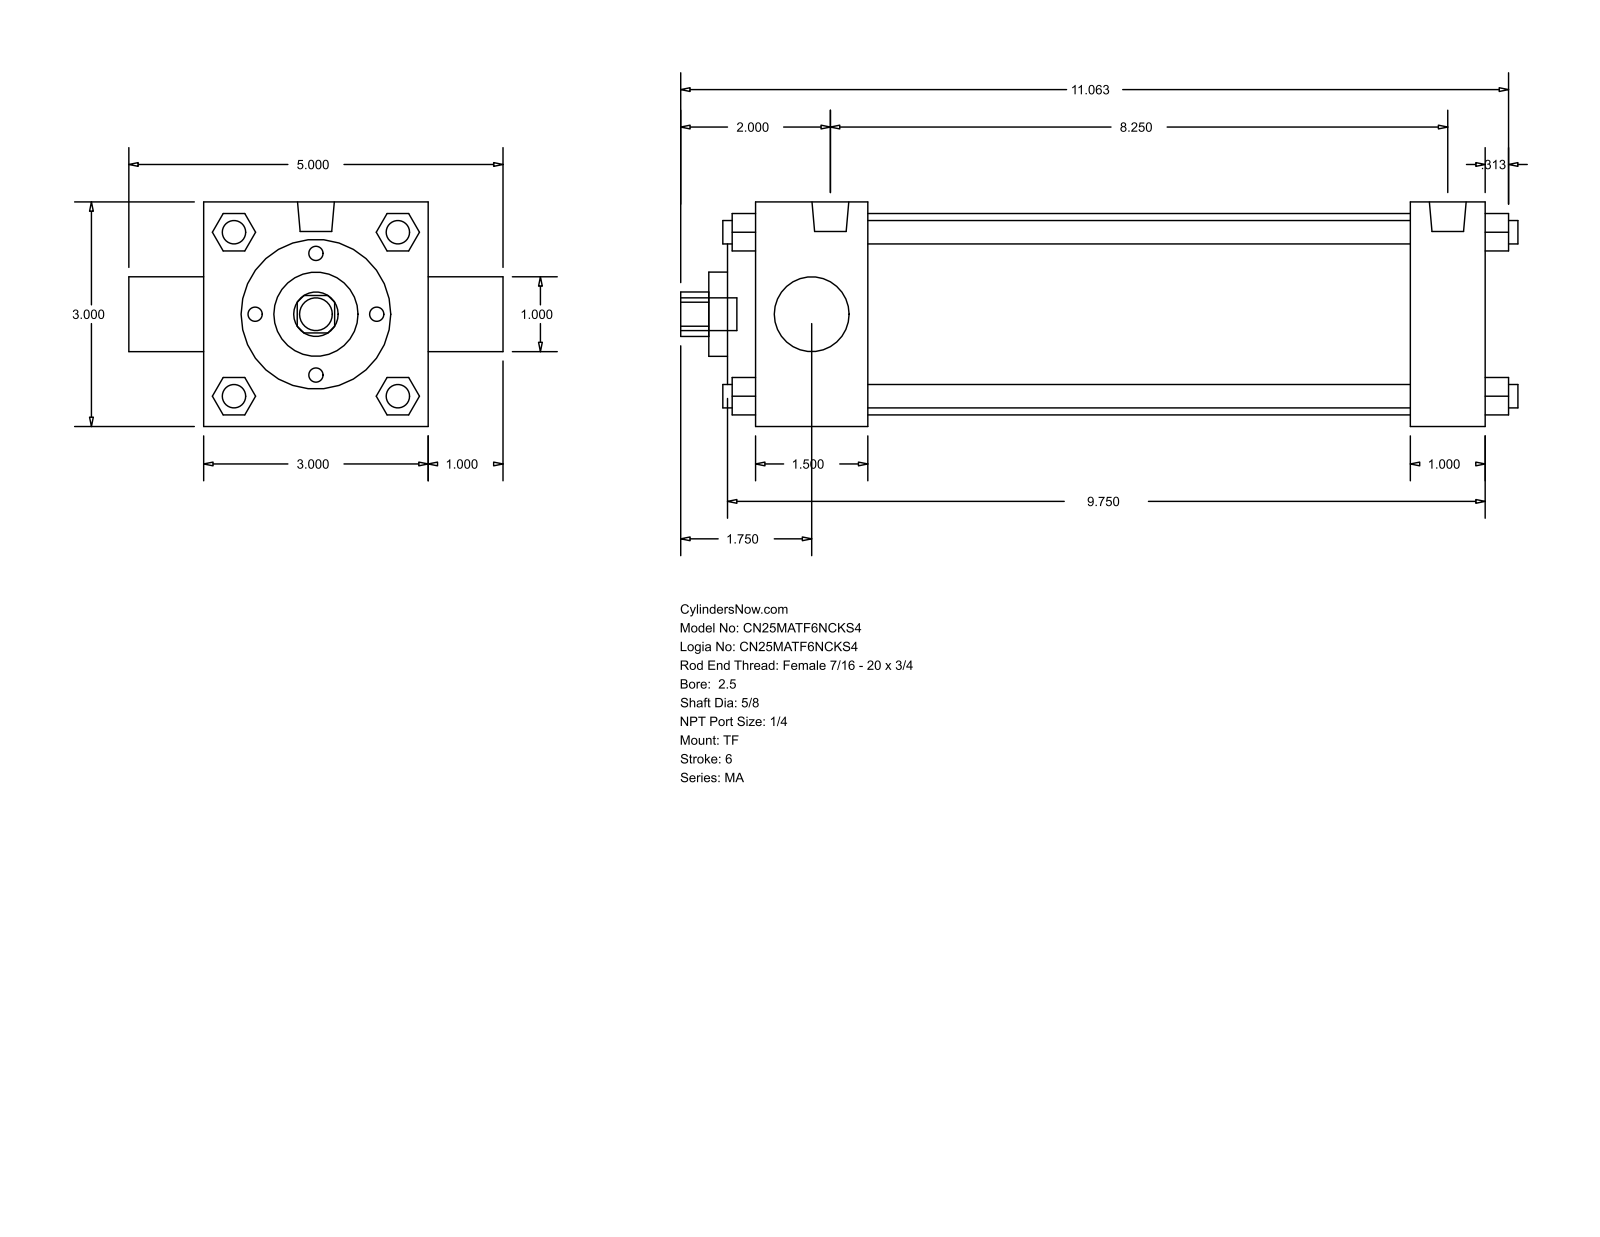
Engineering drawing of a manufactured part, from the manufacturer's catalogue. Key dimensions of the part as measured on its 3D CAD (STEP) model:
Part name (STEP PRODUCT): MA_TF__0250_0.625
STEP written by: GSSL Pune (CONFIG_CONTROL_DESIGN)
Units: millimetres
Bodies: 0 solids, 122 faces (93 planar, 29 cylindrical, 0 other)
Overall size (bounding box): 284.16 × 127 × 76.2
Round holes (diameter × count): ⌀15.88 ×1, ⌀25.4 ×1, ⌀28.57 ×1, ⌀50.8 ×1, ⌀68.33 ×1
Round bosses / shafts (diameter × count): ⌀7.94 ×7, ⌀12.49 ×2, ⌀11.11 ×1
Partial cylindrical surfaces — rounded edges, fillets, slot ends (radius × count): R7.54 ×1
Main face-to-face distances: 76.2, 247.65, 25.4, 38.1, 222.25, 184.15, 209.55, 12.7, 9.52, 47.62
